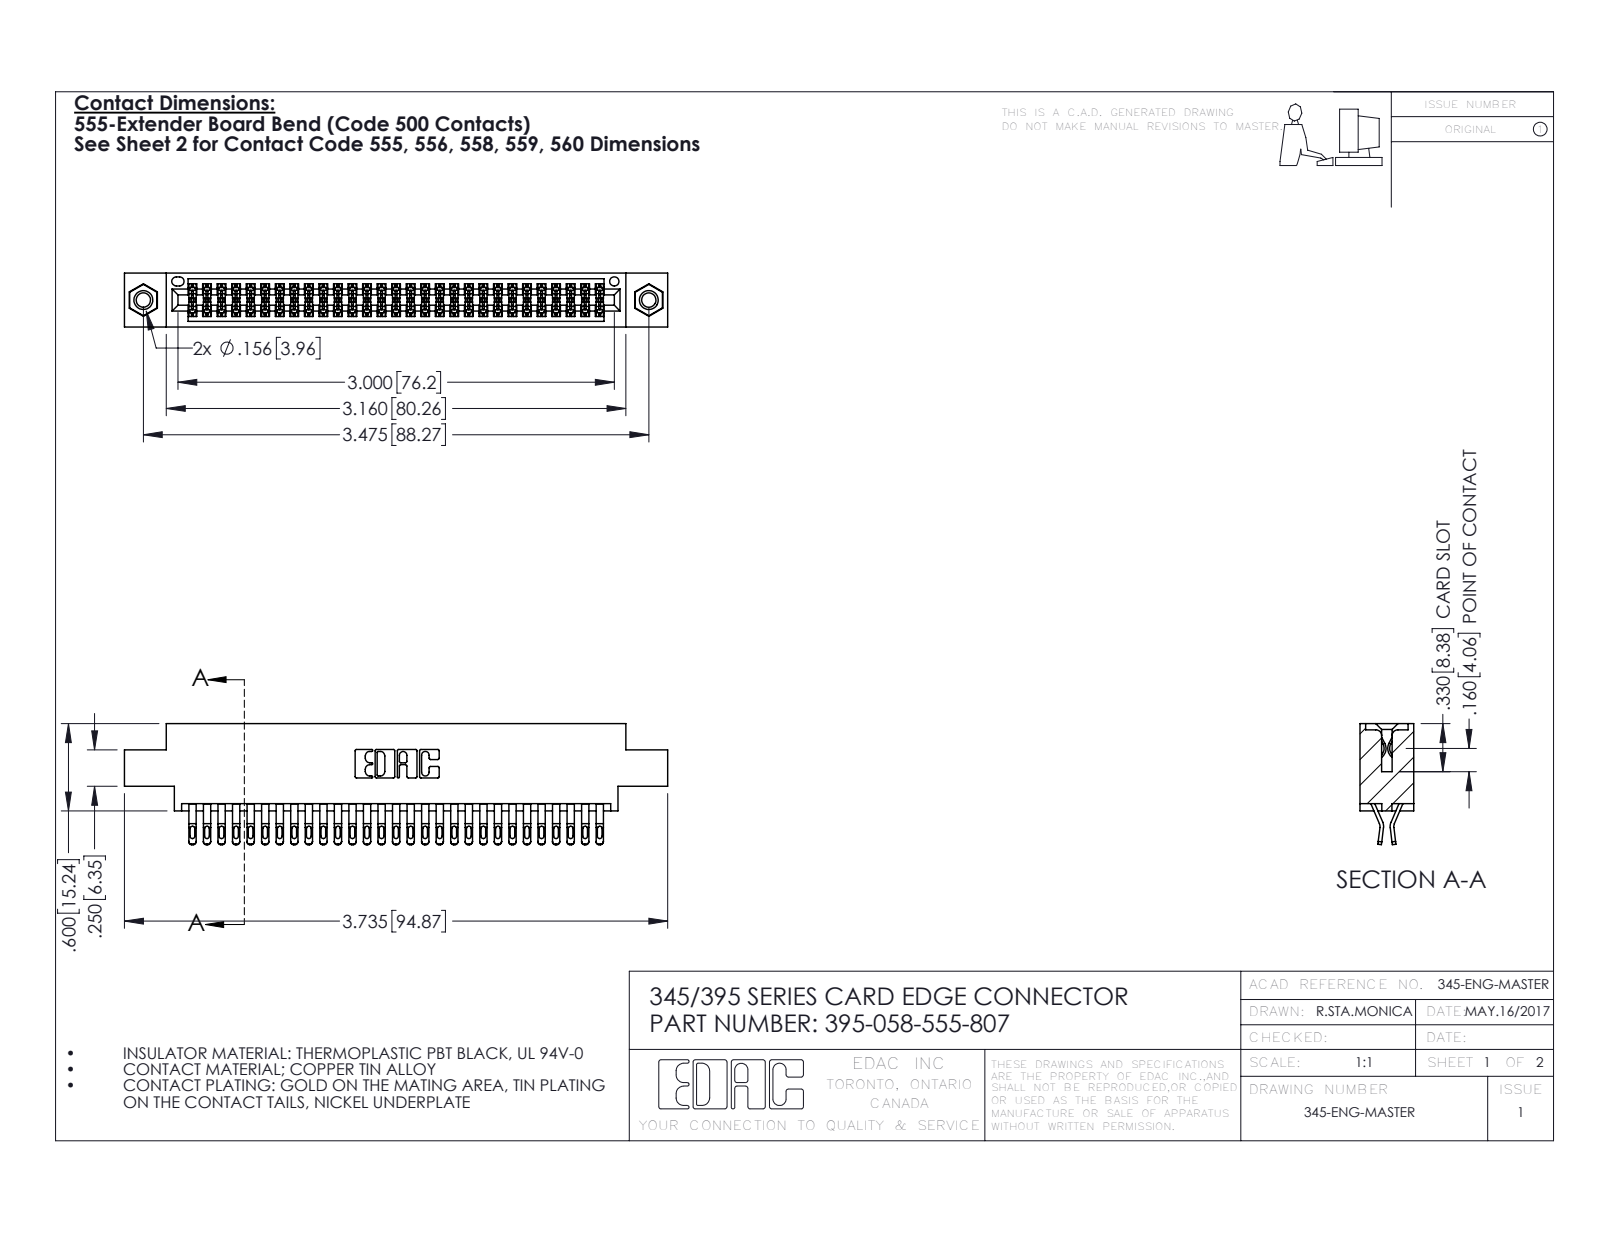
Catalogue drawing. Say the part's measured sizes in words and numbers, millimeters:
The part is named "345 Part_0.170 Offset - 0.156 Dia-TI; 345-250-001_345-250-005-103; 345-292-001_555 Tail; 395-058-555-807". Its 3-D file was written by "SolidWorks 2016 (CONFIG_CONTROL_DESIGN)". It is 61 solids with 3438 faces: 1914 planar, 1508 cylindrical and 16 other. Overall it measures 94.9 by 21.1 by 9.4 millimeters. Its volume is 9 140 cubic millimeters and its surface area 14 010 square millimeters. Round holes: 2 of diameter 2.5, 2 of diameter 3.2, 2 of diameter 4, 1 of diameter 1.6. Round bosses or shafts: 2 of diameter 3.9. Partial cylindrical surfaces (rounded edges, fillets, slot ends): 145 of radius 0.4, 116 of radius 0.5, 87 of radius 0.2, 22 of radius 0.3, 6 of radius 0.2, 6 of radius 0.8, 3 of radius 0.7, 2 of radius 0.3. The main face-to-face distances are 1.8, 7.6, 9.4, 0.6, 5.1, 2.5, 6.9, 5.7, 4.4, 3.8. The hole center spacings are 6.9, 82.3, 88.3.
